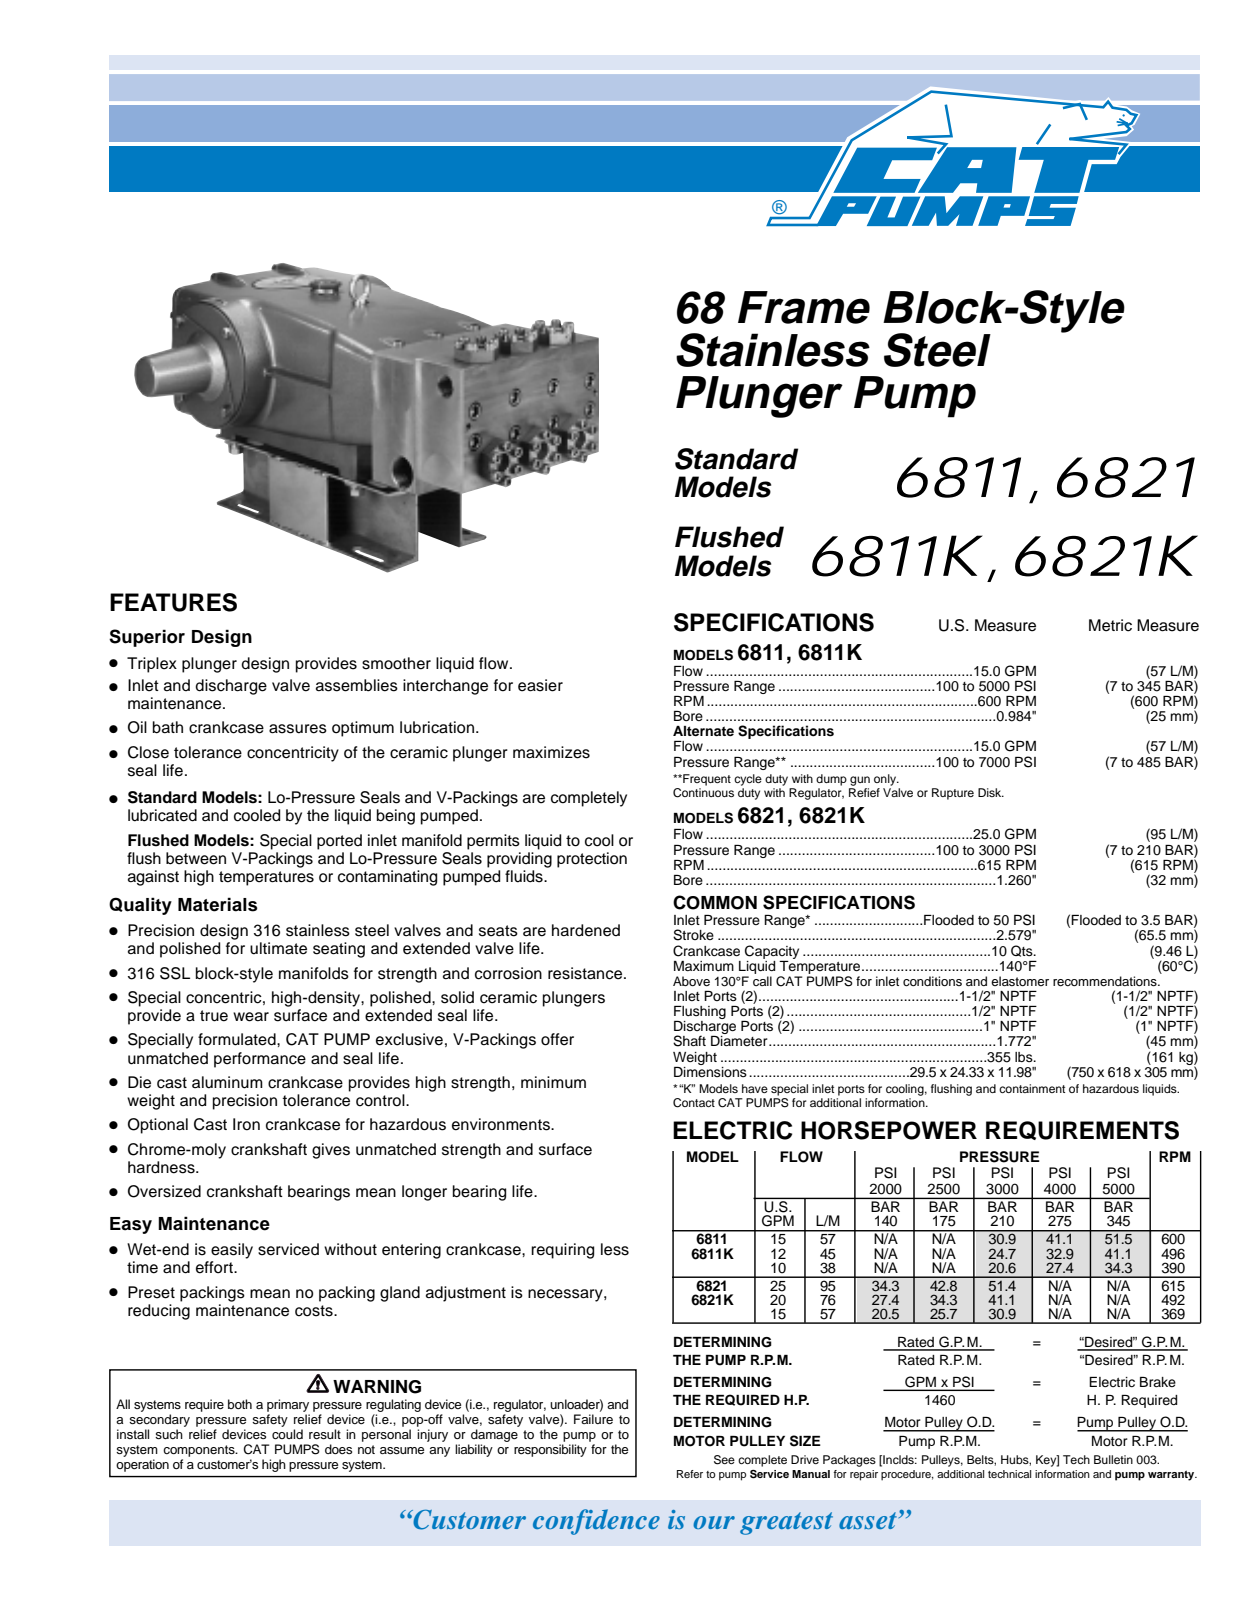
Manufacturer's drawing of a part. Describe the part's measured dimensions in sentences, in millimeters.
The part is named "6811". Its 3-D file was written by "SolidWorks 2021 (CONFIG_CONTROL_DESIGN)". It is 0 solids with 1865 faces: 688 planar, 482 cylindrical and 695 other. Overall it measures 753 by 610 by 306 millimeters. Round holes: 8 of diameter 26, 4 of diameter 13.8, 4 of diameter 19, 3 of diameter 11.5, 2 of diameter 8.5, 1 of diameter 6.8, 1 of diameter 8.6, 1 of diameter 10.2, 1 of diameter 15, 1 of diameter 29, 1 of diameter 42, 1 of diameter 43.7. Round bosses or shafts: 36 of diameter 16, 12 of diameter 18.4, 12 of diameter 18, 8 of diameter 24, 1 of diameter 206, 1 of diameter 45, 1 of diameter 27.5, 1 of diameter 22. Partial cylindrical surfaces (rounded edges, fillets, slot ends): 74 of radius 3, 27 of radius 10, 8 of radius 5, 8 of radius 20, 8 of radius 1800, 6 of radius 4.5, 6 of radius 34.7, 4 of radius 4. The main face-to-face distances are 95, 37, 341, 195, 100, 180, 6, 304, 42, 174. The hole center spacings are 85, 85.1, 98.6, 99.9, 137, 170.1, 177.2, 170.
